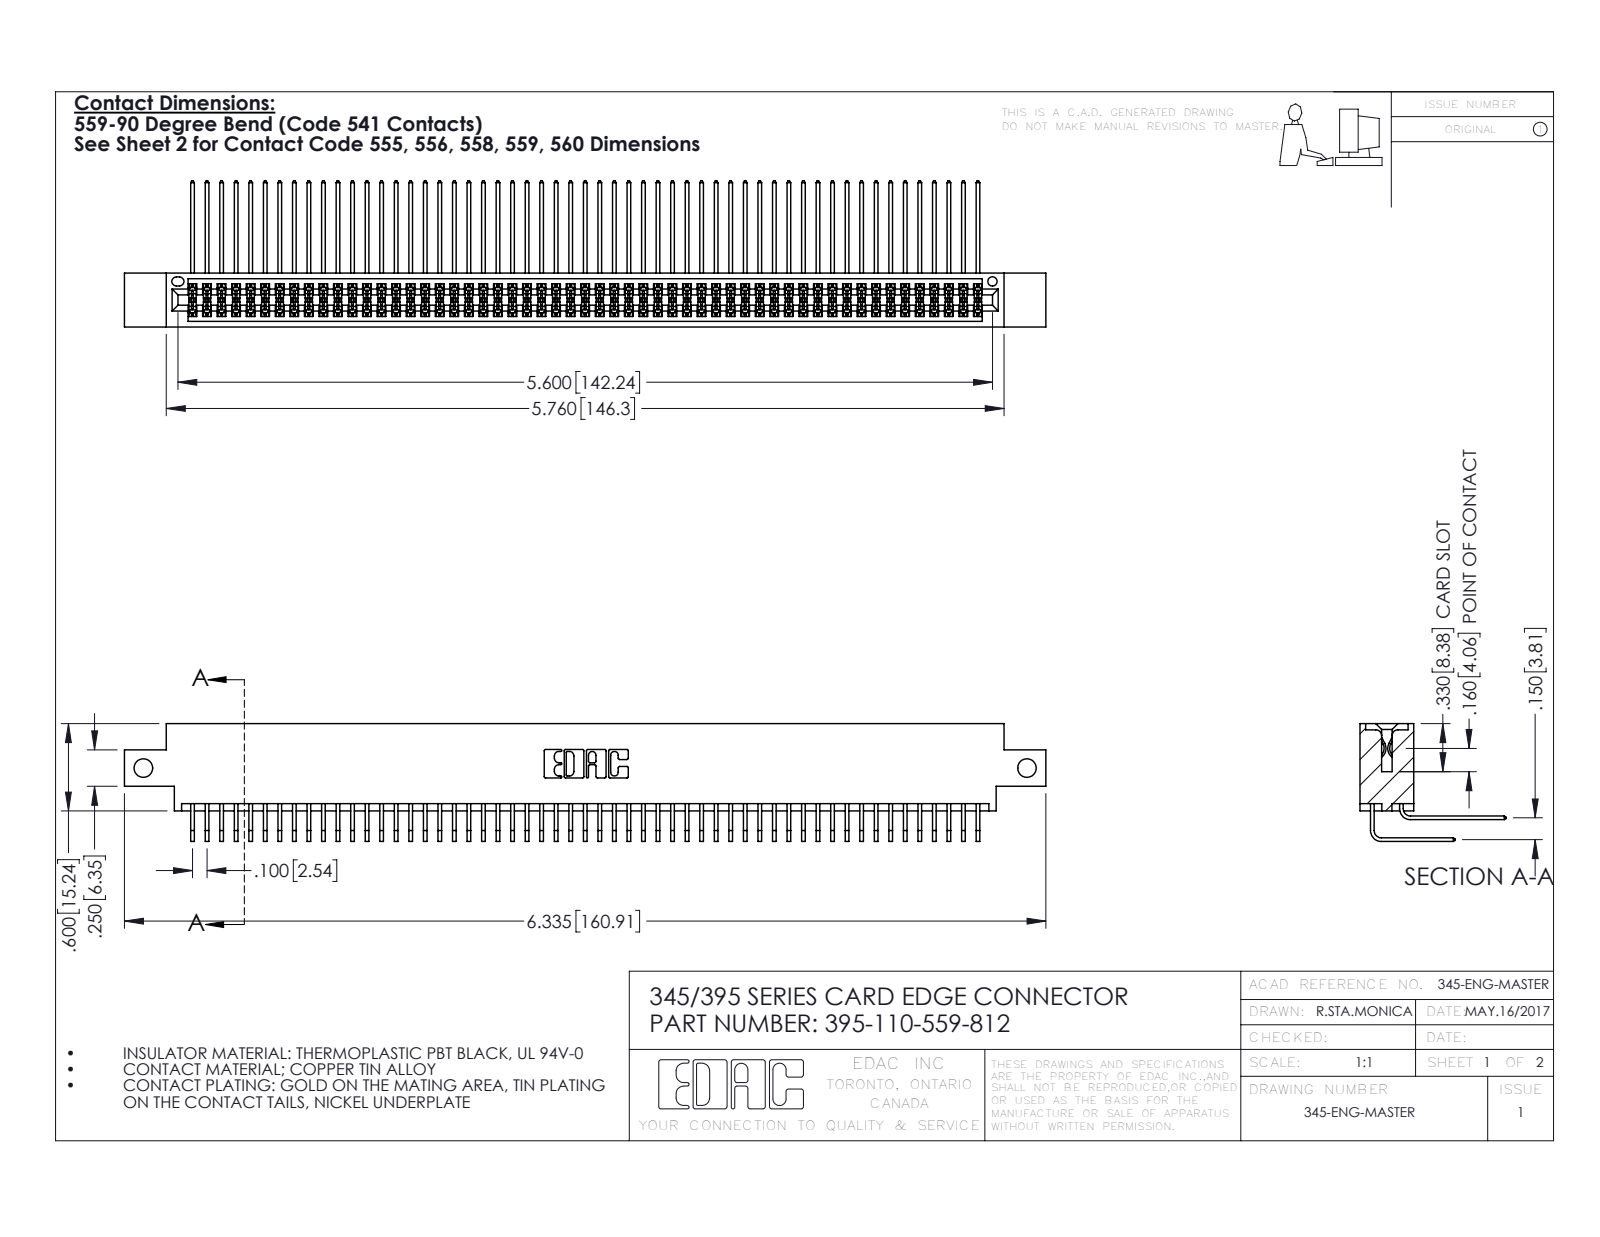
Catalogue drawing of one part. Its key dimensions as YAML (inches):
part_name: "345-292-001_558 559 Tail - 1; 395-110-559-812; 345-292-001_559 Tail - 2; 345 Part_0.170 Offset - Side Mount"
step_written_by: "SolidWorks 2016 (CONFIG_CONTROL_DESIGN)"
units: inches
bodies: {solids: 111, faces: 5850, planar: 3934, cylindrical: 1916, other: 0}
overall_size: [6.335, 1.005, 0.809]
volume: 0.988
surface_area: 42.11
round_holes:
  - {diameter: 0.128, count: 2}
  - {diameter: 0.064, count: 1}
partial_cylinders:
  - {radius: 0.006, count: 165}
  - {radius: 0.01, count: 22}
  - {radius: 0.007, count: 6}
  - {radius: 0.031, count: 6}
  - {radius: 0.026, count: 3}
  - {radius: 0.014, count: 2}
  - {radius: 0.019, count: 2}
  - {radius: 0.022, count: 2}
face_to_face_distances: [0.072, 0.298, 0.37, 0.2, 0.098, 0.272, 0.025, 0.225, 0.175, 0.15]
hole_center_spacings: [6.075]
